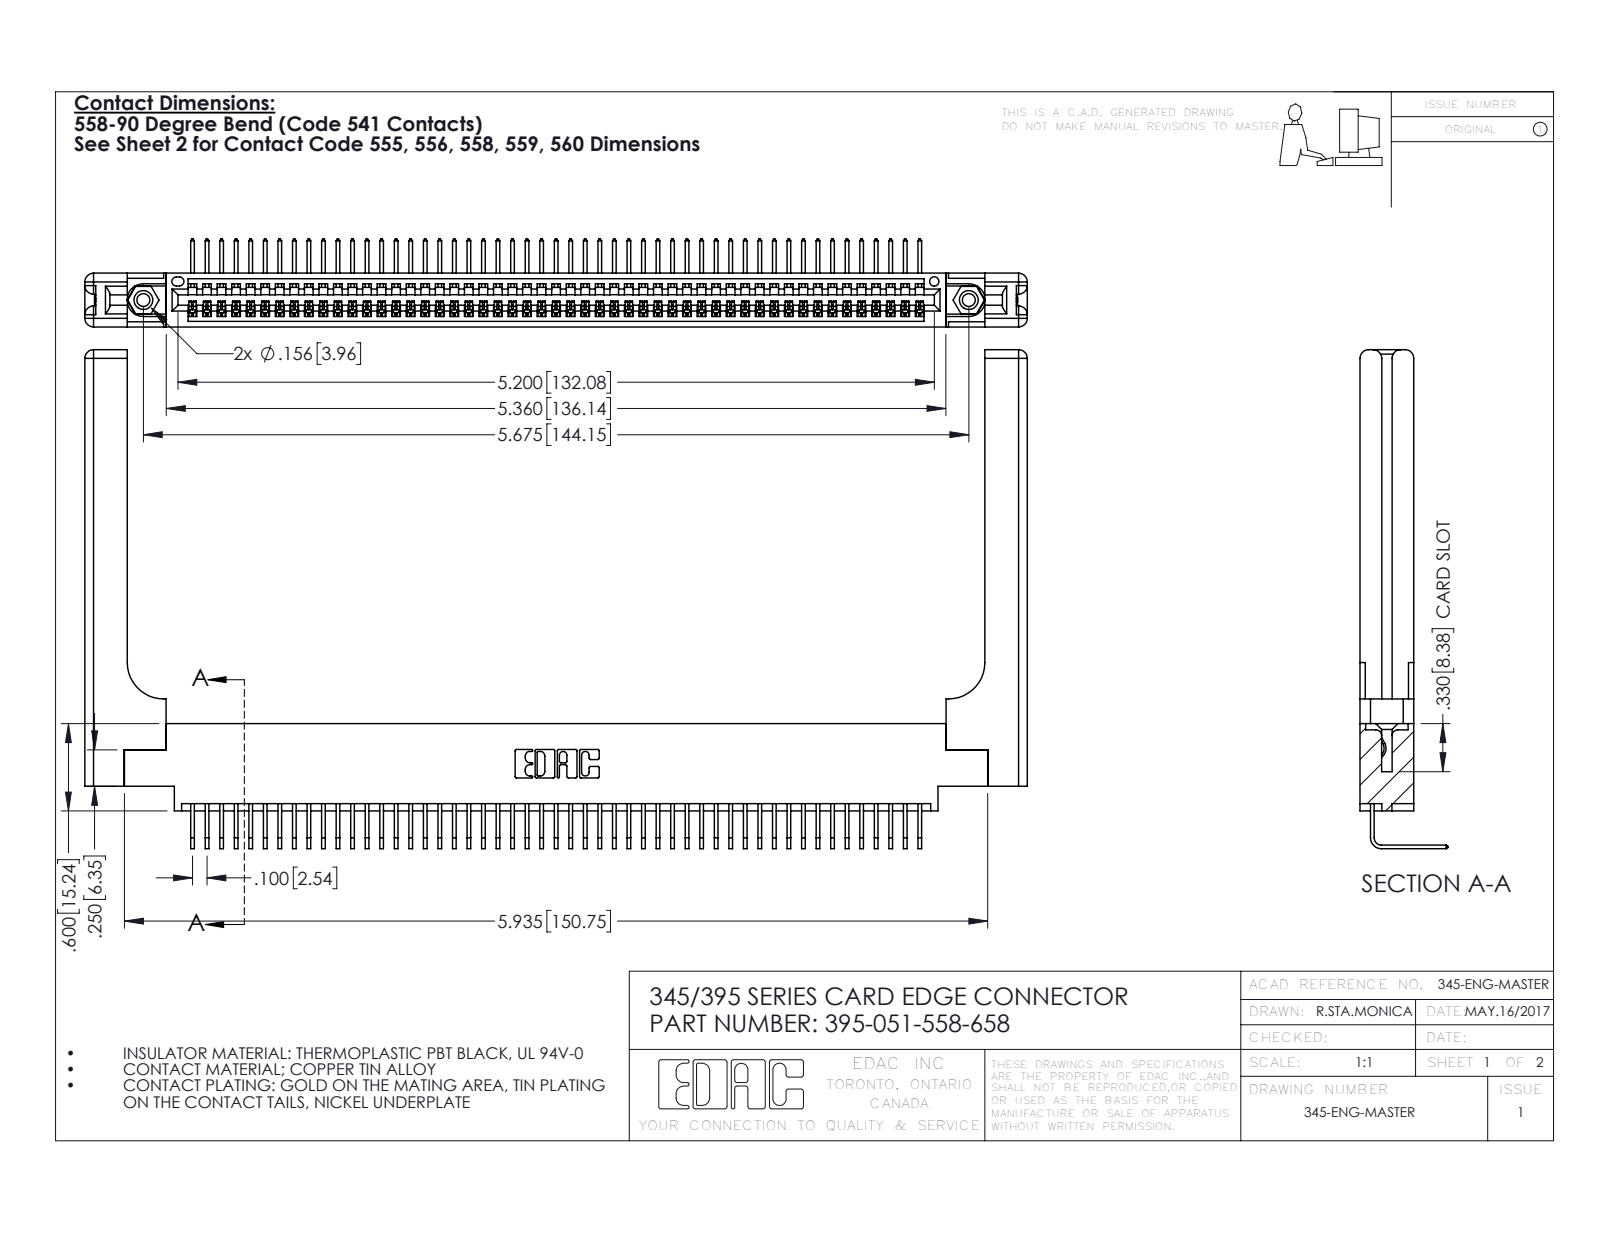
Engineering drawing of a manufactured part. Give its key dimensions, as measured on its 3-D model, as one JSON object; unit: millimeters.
{"part_name": "345-250-001_345-250-001-102; 395-051-558-658; 345-292-001_558 Tail - 2; 345-220-058_345-220-058 (+1 more)", "step_written_by": "SolidWorks 2016 (CONFIG_CONTROL_DESIGN)", "units": "millimeters", "bodies": {"solids": 56, "faces": 3446, "planar": 2374, "cylindrical": 1012, "other": 60}, "overall_size": [164.6, 87.1, 15.4], "volume_mm3": 24270, "surface_area_mm2": 27500, "round_holes": [[2.3, 2], [3.2, 2], [4, 2], [1.6, 1]], "round_bosses_or_shafts": [[3.9, 2]], "partial_cylinders_radius": [[0.2, 102], [0.3, 22], [1.5, 16], [0.2, 6], [0.8, 6], [0.7, 3], [0.8, 2], [0.8, 2]], "face_to_face_distances": [9.4, 1.8, 7.6, 2.5, 6.9, 0.6, 5.1, 5.7, 3.8, 3.8], "hole_center_spacings": [6.9, 138.2, 144.1]}
